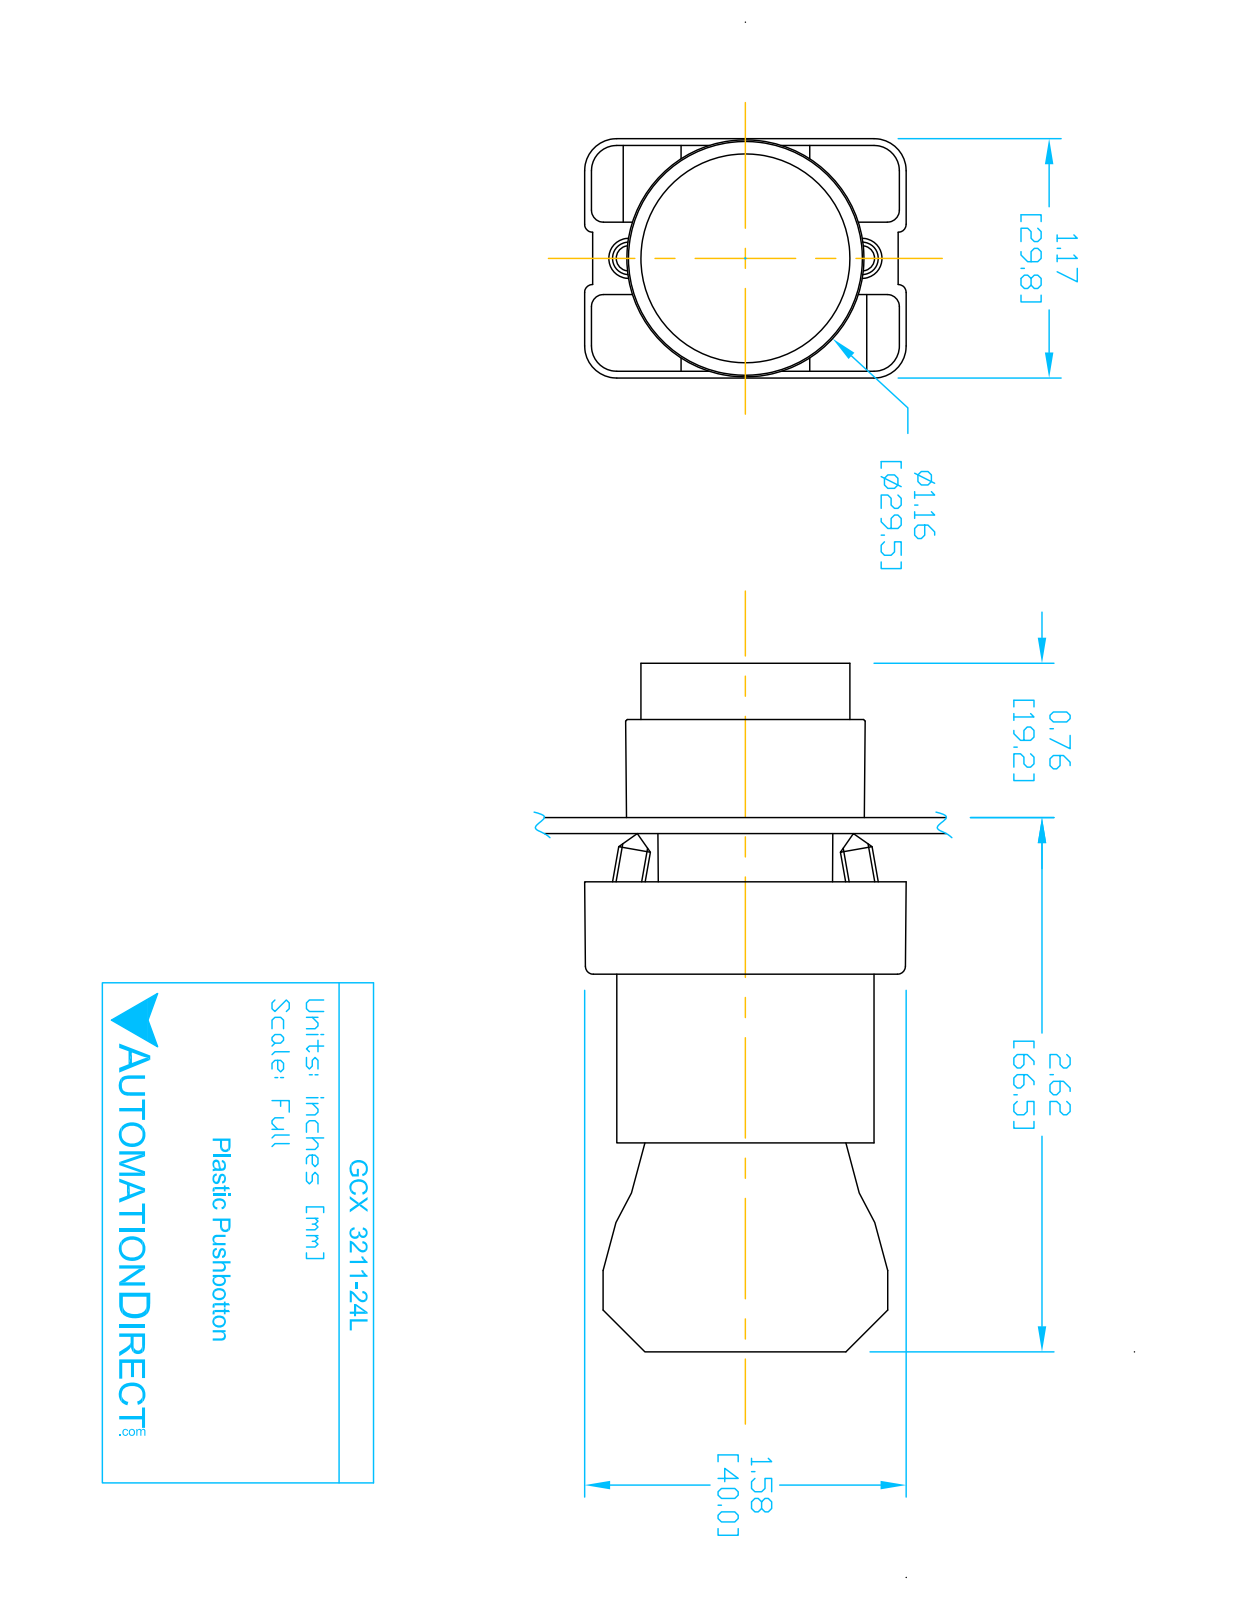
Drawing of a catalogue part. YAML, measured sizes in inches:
part_name: "GCX3211L OPERATOR; GCX3211-24L; ECX3029-2; ECX1050 (+1 more)"
step_written_by: "SolidWorks 2016 (AUTOMOTIVE_DESIGN)"
units: inches
bodies: {solids: 7, faces: 425, planar: 250, cylindrical: 144, other: 31}
overall_size: [3.319, 1.581, 1.177]
volume: 2.721
surface_area: 36.32
round_holes:
  - {diameter: 0.079, count: 2}
  - {diameter: 0.124, count: 2}
  - {diameter: 0.13, count: 2}
  - {diameter: 0.087, count: 1}
  - {diameter: 0.197, count: 1}
  - {diameter: 0.469, count: 1}
  - {diameter: 0.878, count: 1}
  - {diameter: 0.888, count: 1}
  - {diameter: 1.024, count: 1}
round_bosses_or_shafts:
  - {diameter: 0.157, count: 4}
  - {diameter: 1.175, count: 1}
  - {diameter: 1.004, count: 1}
  - {diameter: 0.945, count: 1}
  - {diameter: 0.856, count: 1}
  - {diameter: 0.78, count: 1}
  - {diameter: 0.504, count: 1}
partial_cylinders:
  - {radius: 0.059, count: 24}
  - {radius: 0.041, count: 12}
  - {radius: 0.124, count: 12}
  - {radius: 0.157, count: 12}
  - {radius: 0.039, count: 8}
  - {radius: 0.128, count: 2}
  - {radius: 0.02, count: 1}
  - {radius: 0.063, count: 1}
face_to_face_distances: [0.827, 0.579, 1.171, 2.02, 1.193, 0.031, 0.033, 0.573, 1.165, 0.593]
hole_center_spacings: [0.236, 0.544, 0.472, 0.49]
